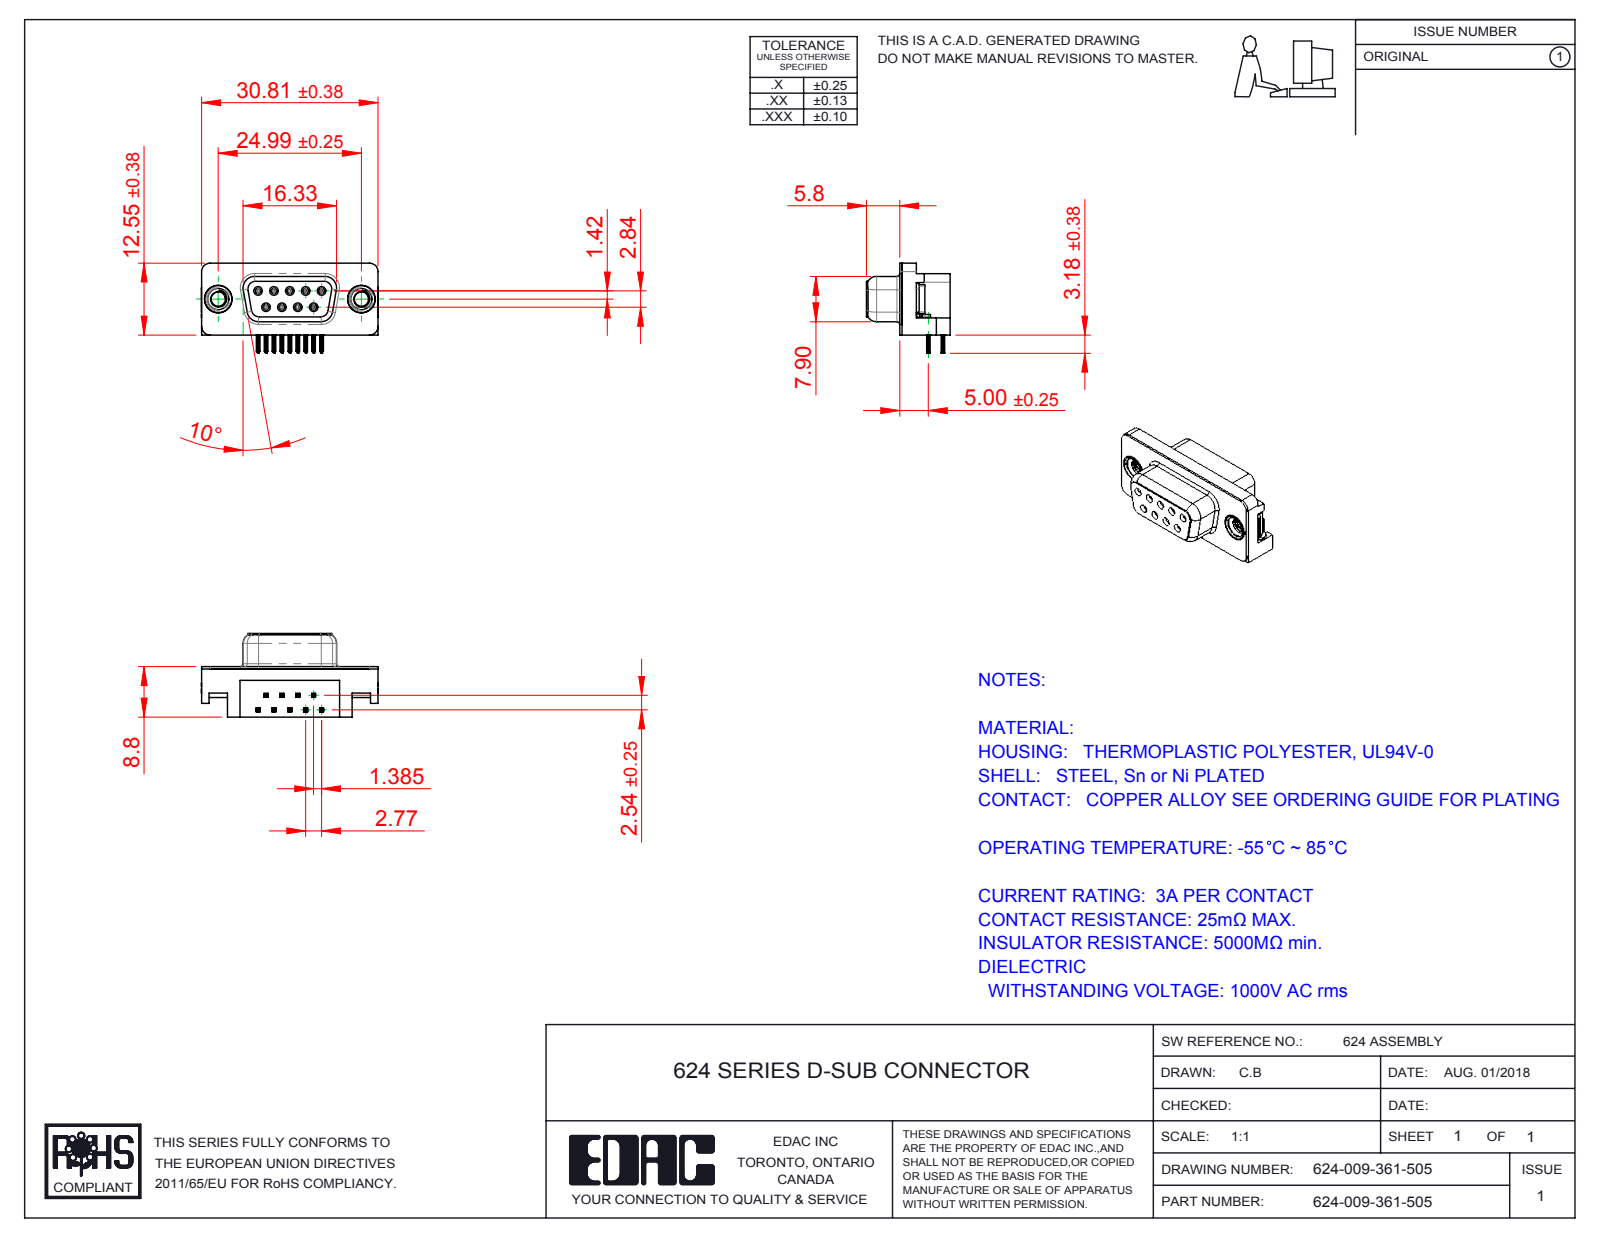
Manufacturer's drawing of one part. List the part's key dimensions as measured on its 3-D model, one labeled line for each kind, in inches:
Part name (STEP PRODUCT): 624-009-361-505; 624 M3 Threaded Rivet; 624 Non Board Mount; 624 Contact Top (+3 more)
STEP written by: SolidWorks 2016 (CONFIG_CONTROL_DESIGN)
Units: inches
Bodies: 15 solids, 1520 faces (642 planar, 410 cylindrical, 468 other)
Overall size (bounding box): 1.216 × 0.619 × 0.575
Volume: 0.179 in³ · Surface area: 6.724 in²
Round holes (diameter × count): ⌀0.031 ×9, ⌀0.035 ×9, ⌀0.098 ×2, ⌀0.157 ×2, ⌀0.189 ×2, ⌀0.197 ×2
Round bosses / shafts (diameter × count): ⌀0.047 ×9, ⌀0.193 ×2, ⌀0.187 ×2, ⌀0.154 ×2
Partial cylindrical surfaces — rounded edges, fillets, slot ends (radius × count): R0.004 ×72, R0.006 ×36, R0.014 ×18, R0.039 ×18, R0.013 ×9, R0.01 ×8, R0.053 ×8, R0.059 ×7
Main face-to-face distances: 0.016, 0.331, 0.346, 0.114, 0.098, 0.244, 0.232, 0.014, 0.421, 0.407
Hole centre spacings: 0.124, 0.109, 0.218, 0.198, 0.198, 0.327, 0.294, 0.295
